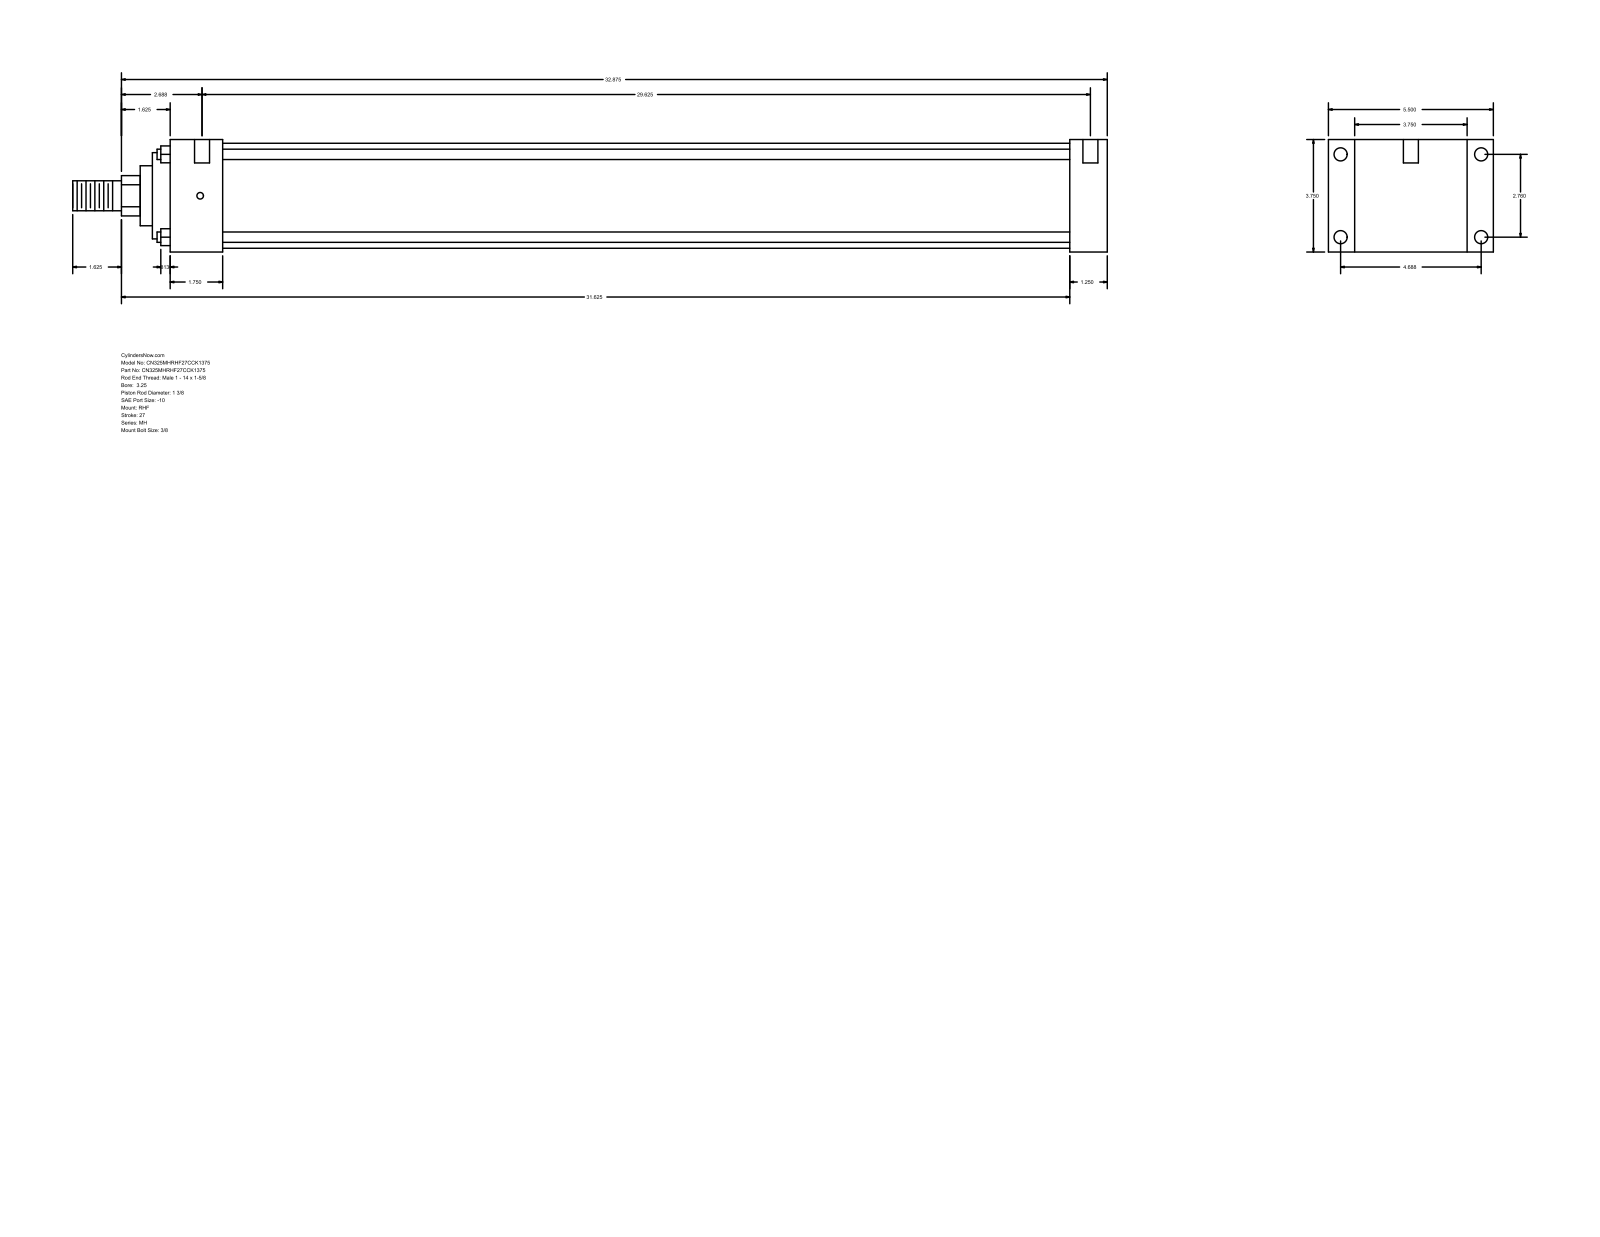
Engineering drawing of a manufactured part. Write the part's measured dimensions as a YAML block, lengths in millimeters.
part_name: "MH_RHF__0325_1.375"
step_written_by: "GSSL Pune (CONFIG_CONTROL_DESIGN)"
units: millimeters
bodies: {solids: 0, faces: 90, planar: 61, cylindrical: 29, other: 0}
overall_size: [876.3, 139.7, 95.25]
round_holes:
  - {diameter: 5.56, count: 4}
  - {diameter: 11.13, count: 4}
  - {diameter: 12.7, count: 2}
round_bosses_or_shafts:
  - {diameter: 8.76, count: 4}
  - {diameter: 88.9, count: 1}
  - {diameter: 73.03, count: 1}
  - {diameter: 50.8, count: 1}
  - {diameter: 34.92, count: 1}
  - {diameter: 25.4, count: 1}
partial_cylinders:
  - {radius: 17.06, count: 1}
face_to_face_distances: [95.24, 31.75, 22.23, 117.47, 762, 793.75, 139.7, 44.45, 717.55, 749.3]
hole_center_spacings: [70.1, 119.06, 138.16, 758.83, 1.59, 4.76, 752.48, 754.07]
